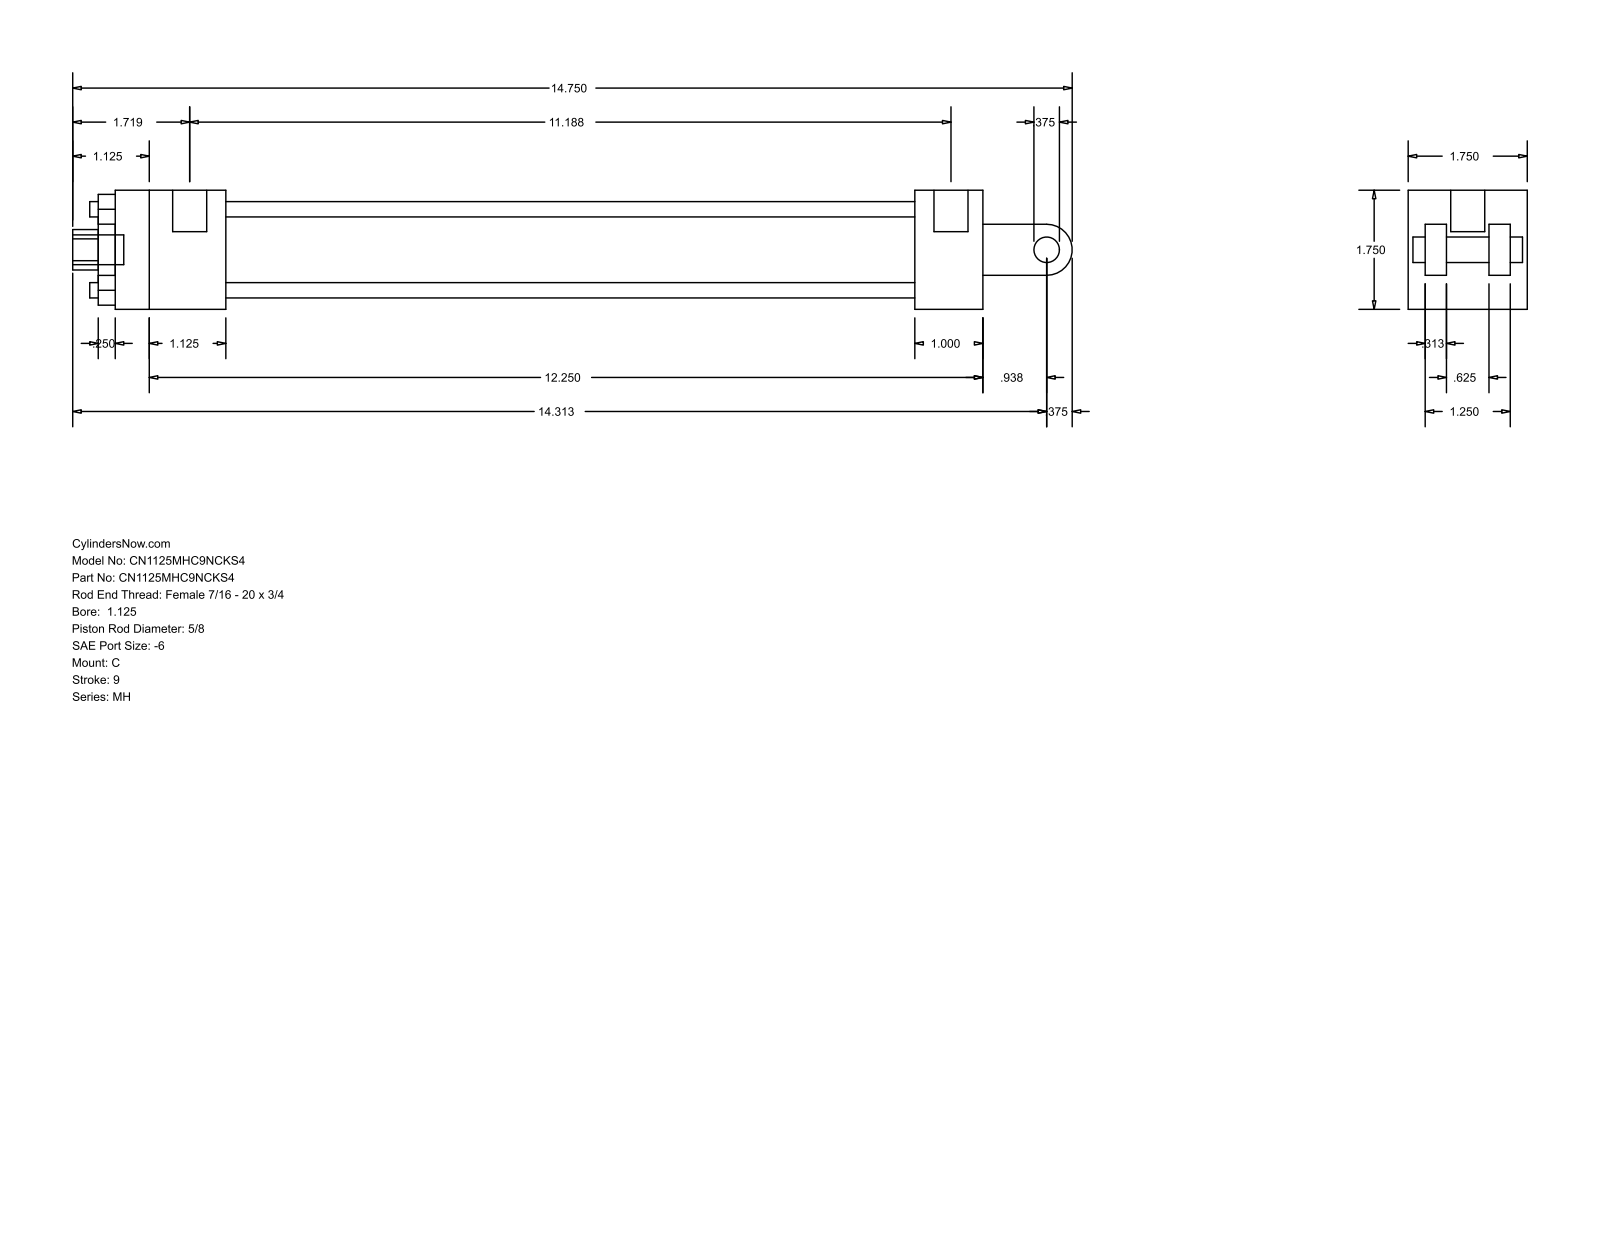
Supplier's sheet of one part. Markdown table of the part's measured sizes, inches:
| quantity | value |
| --- | --- |
| part name | MH_C__0112_0.625 |
| STEP written by | GSSL Pune (CONFIG_CONTROL_DESIGN) |
| units | inches |
| bodies | 0 solids, 99 faces (70 planar, 29 cylindrical, 0 other) |
| overall size | 14.687 × 1.75 × 1.75 |
| round holes (diameter × count) | 0.225 × 4, 0.219 × 2, 0.5 × 1, 0.625 × 1, 1.125 × 1, 1.375 × 1 |
| round bosses / shafts (diameter × count) | 0.219 × 2, 0.5 × 1, 0.437 × 1, 0.375 × 1 |
| partial cylindrical surfaces (radius × count) | 0.297 × 1, 0.375 × 1 |
| main face-to-face distances | 1.75, 0.25, 1.25, 0.563, 0.5, 1.188, 1.5, 0.313, 0.938, 1.625 |
| hole center spacings | 0.841, 1.19, 1.683 |
